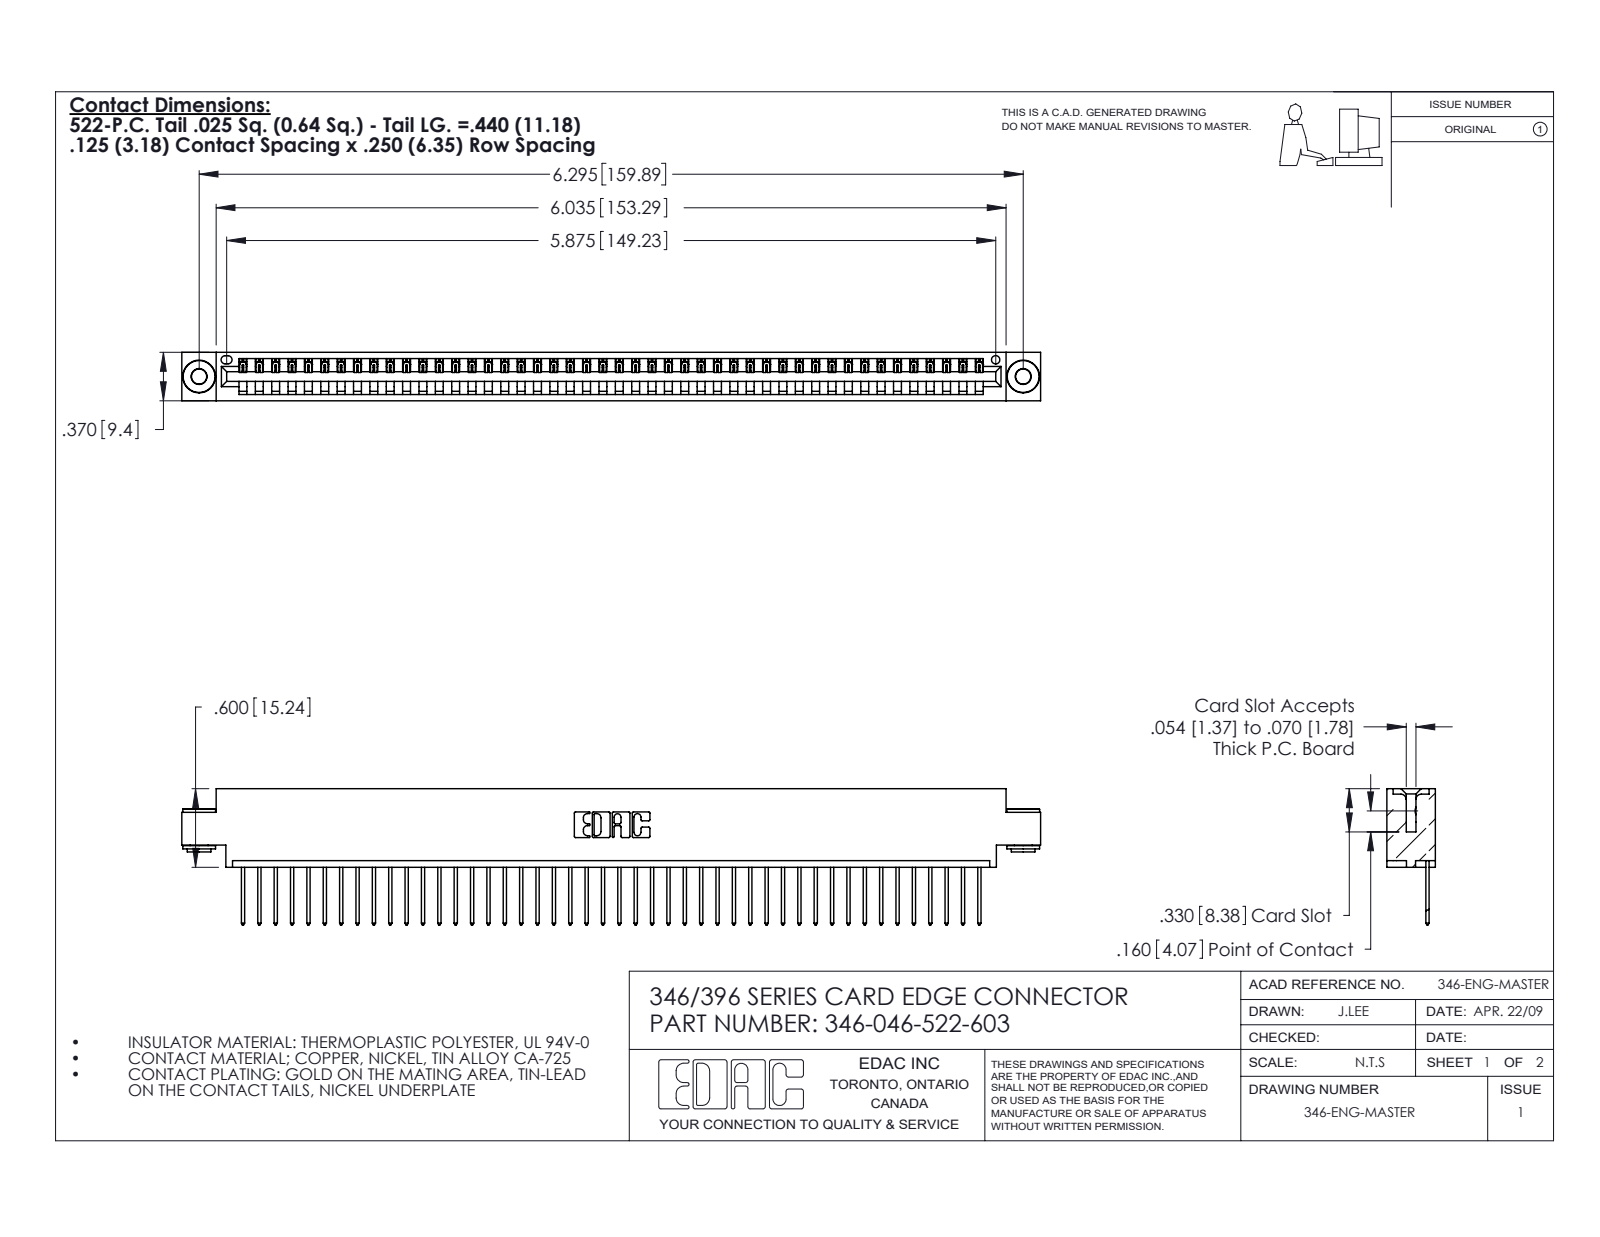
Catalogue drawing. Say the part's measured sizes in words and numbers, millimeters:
The part is named "346 Part_0.170 Offset - 0.156 Dia-TH; 346-046-522-603; 345-292-001_345-293-122; 345-250-002_345-250-002-102". Its 3-D file was written by "SolidWorks 2020 (CONFIG_CONTROL_DESIGN)". It is 49 solids with 2846 faces: 1944 planar, 894 cylindrical and 8 other. Overall it measures 166.6 by 26.4 by 9.4 millimeters. Its volume is 15 800 cubic millimeters and its surface area 20 410 square millimeters. Round holes: 2 of diameter 2.9, 2 of diameter 4, 1 of diameter 1.6. Round bosses or shafts: 2 of diameter 6.4, 2 of diameter 4.6, 2 of diameter 3.5. Partial cylindrical surfaces (rounded edges, fillets, slot ends): 92 of radius 0.2, 92 of radius 0.3, 22 of radius 0.3, 6 of radius 0.2, 6 of radius 0.8, 3 of radius 0.7, 2 of radius 0.8, 2 of radius 1. The main face-to-face distances are 1.2, 8.2, 9.4, 6.4, 0.6, 1.8, 7.6, 5.6, 3.8, 2.5. The hole center spacings are 6.2, 154.6, 159.9.
